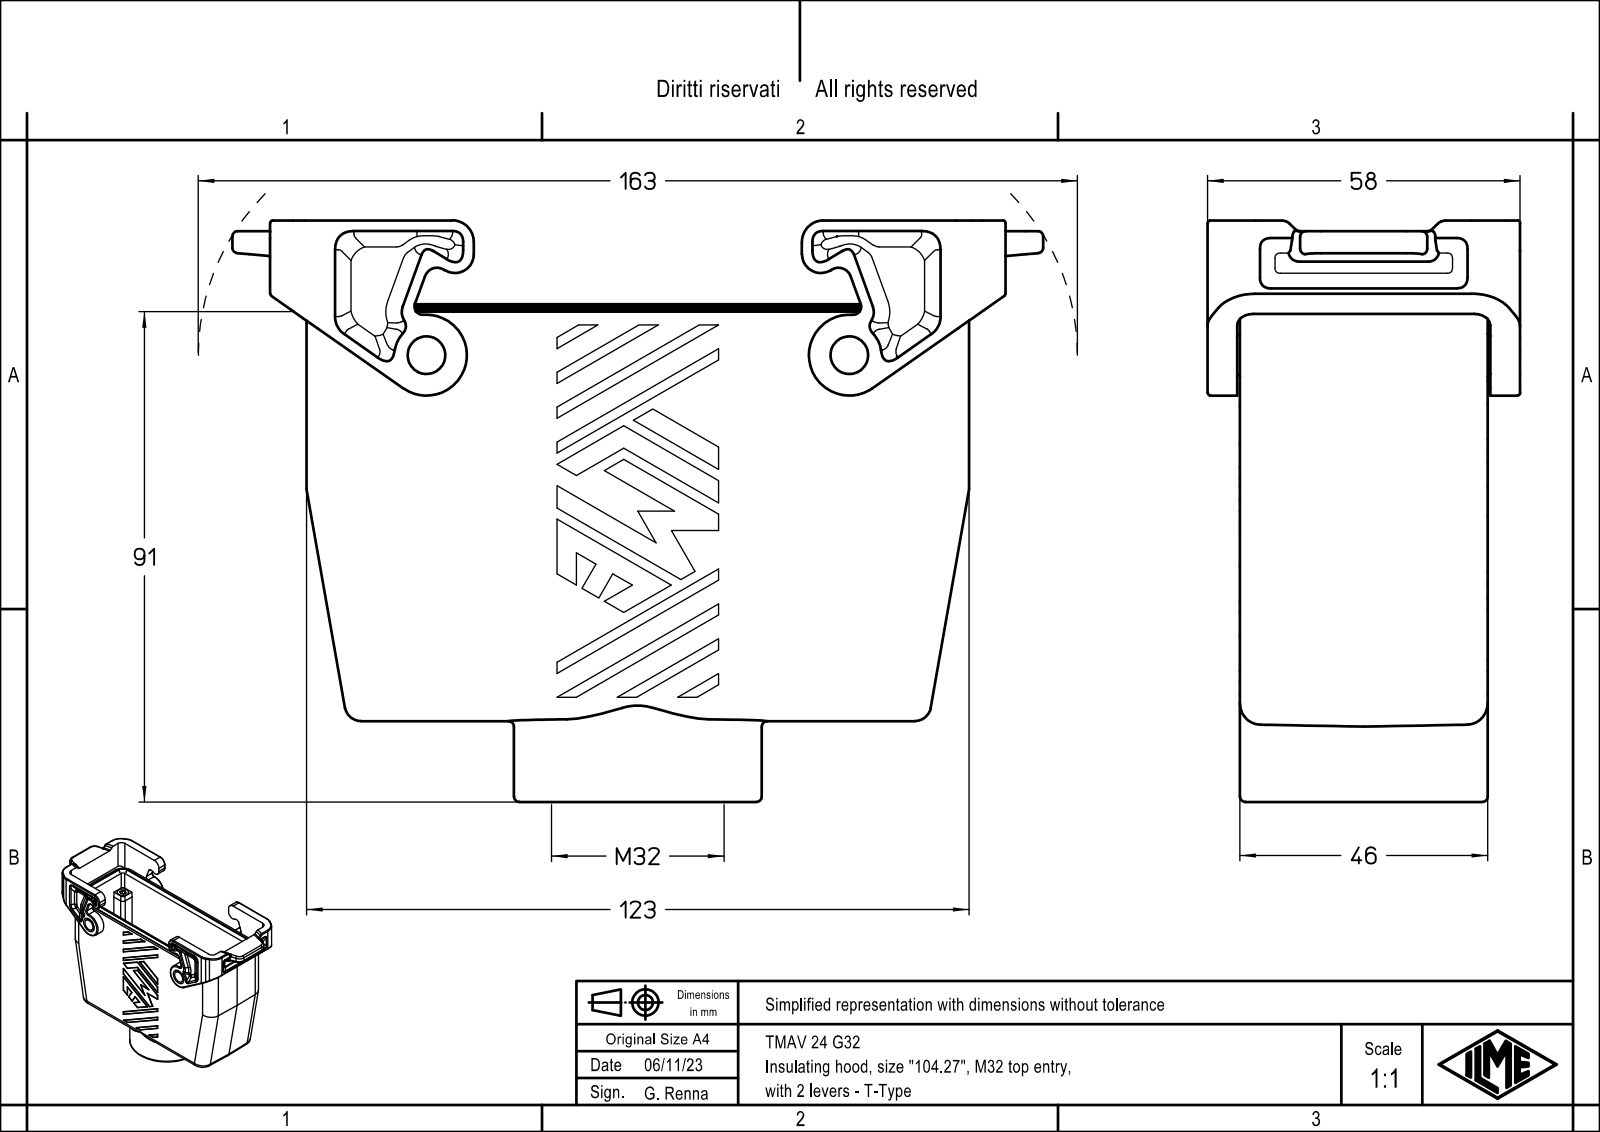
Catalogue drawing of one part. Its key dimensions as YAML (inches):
part_name: "TMAV 24 G32"
step_written_by: "Creo Elements/Direct Modeling 20.1B 02-Apr-2019 (C) Parametric Technology GmbH (AUTOMOTIVE_DESIGN)"
units: inches
bodies: {solids: 1, faces: 562, planar: 218, cylindrical: 282, other: 62}
overall_size: [5.925, 4.248, 2.283]
volume: 11.46
surface_area: 110
round_holes:
  - {diameter: 1.102, count: 1}
  - {diameter: 1.205, count: 1}
round_bosses_or_shafts:
  - {diameter: 0.276, count: 2}
  - {diameter: 1.811, count: 1}
partial_cylinders:
  - {radius: 0.006, count: 88}
  - {radius: 0.118, count: 20}
  - {radius: 0.039, count: 16}
  - {radius: 0.079, count: 16}
  - {radius: 0.059, count: 10}
  - {radius: 0.051, count: 8}
  - {radius: 0.236, count: 8}
  - {radius: 0.276, count: 8}
face_to_face_distances: [0.213, 1.598, 1.386, 1.811, 0.02, 0.232, 1.618, 1.831, 0.217, 2.047]
